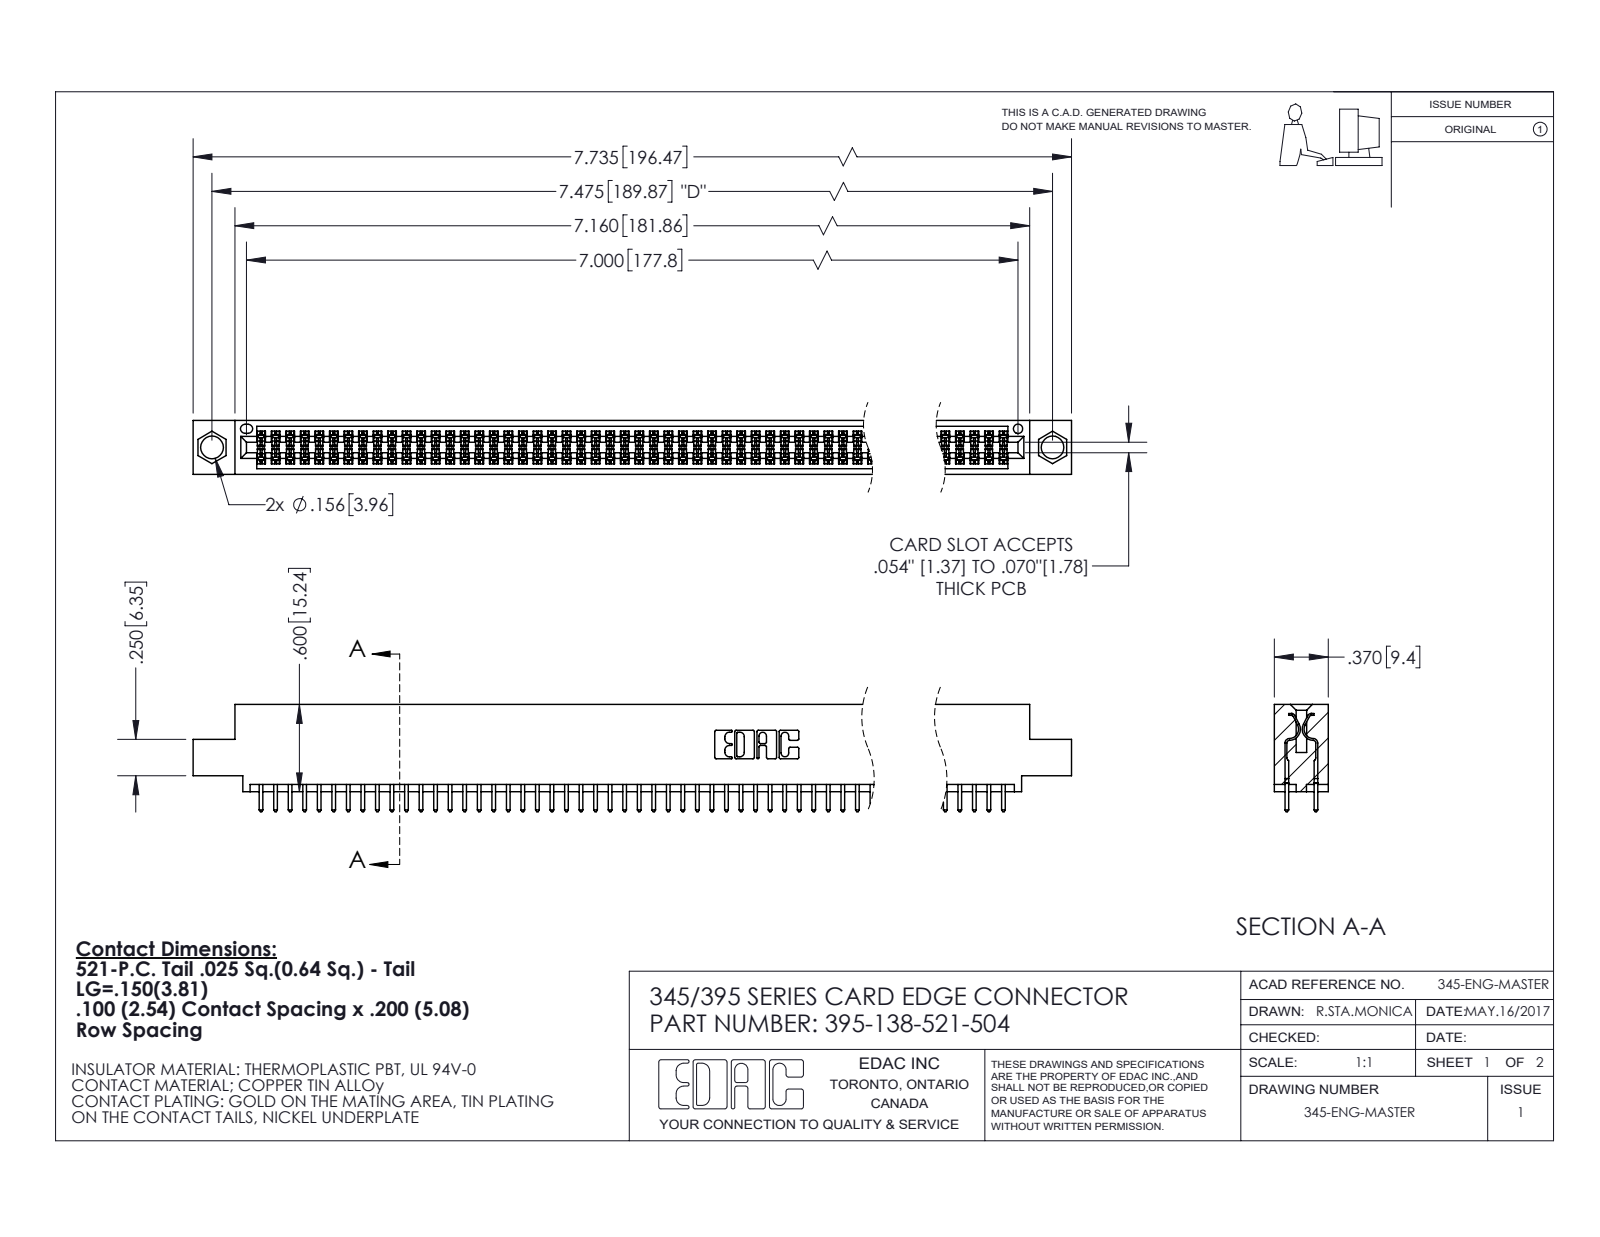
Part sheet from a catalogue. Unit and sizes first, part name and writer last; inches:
Units: inches
Overall size (bounding box): 7.735 × 0.737 × 0.37
Round holes (diameter × count): ⌀0.156 ×2, ⌀0.064 ×1
Partial cylindrical surfaces — rounded edges, fillets, slot ends (radius × count): R0.006 ×207, R0.01 ×138, R0.01 ×22, R0.007 ×6, R0.031 ×6, R0.026 ×3, R0.014 ×2, R0.019 ×2
Main face-to-face distances: 0.072, 0.298, 0.2, 0.098, 0.272, 0.025, 0.37, 0.225, 0.175, 0.149
Hole centre spacings: 0.27, 7.239, 7.475
Volume: 1.166 in³ · Surface area: 43.92 in²
Bodies: 139 solids, 7044 faces (4652 planar, 2392 cylindrical, 0 other)
Part name (STEP PRODUCT): 345-292-001_345-293-121; 345 Part_0.110 Offset - 0.156 Dia-TI; 395-138-521-504
STEP written by: SolidWorks 2020 (CONFIG_CONTROL_DESIGN)
